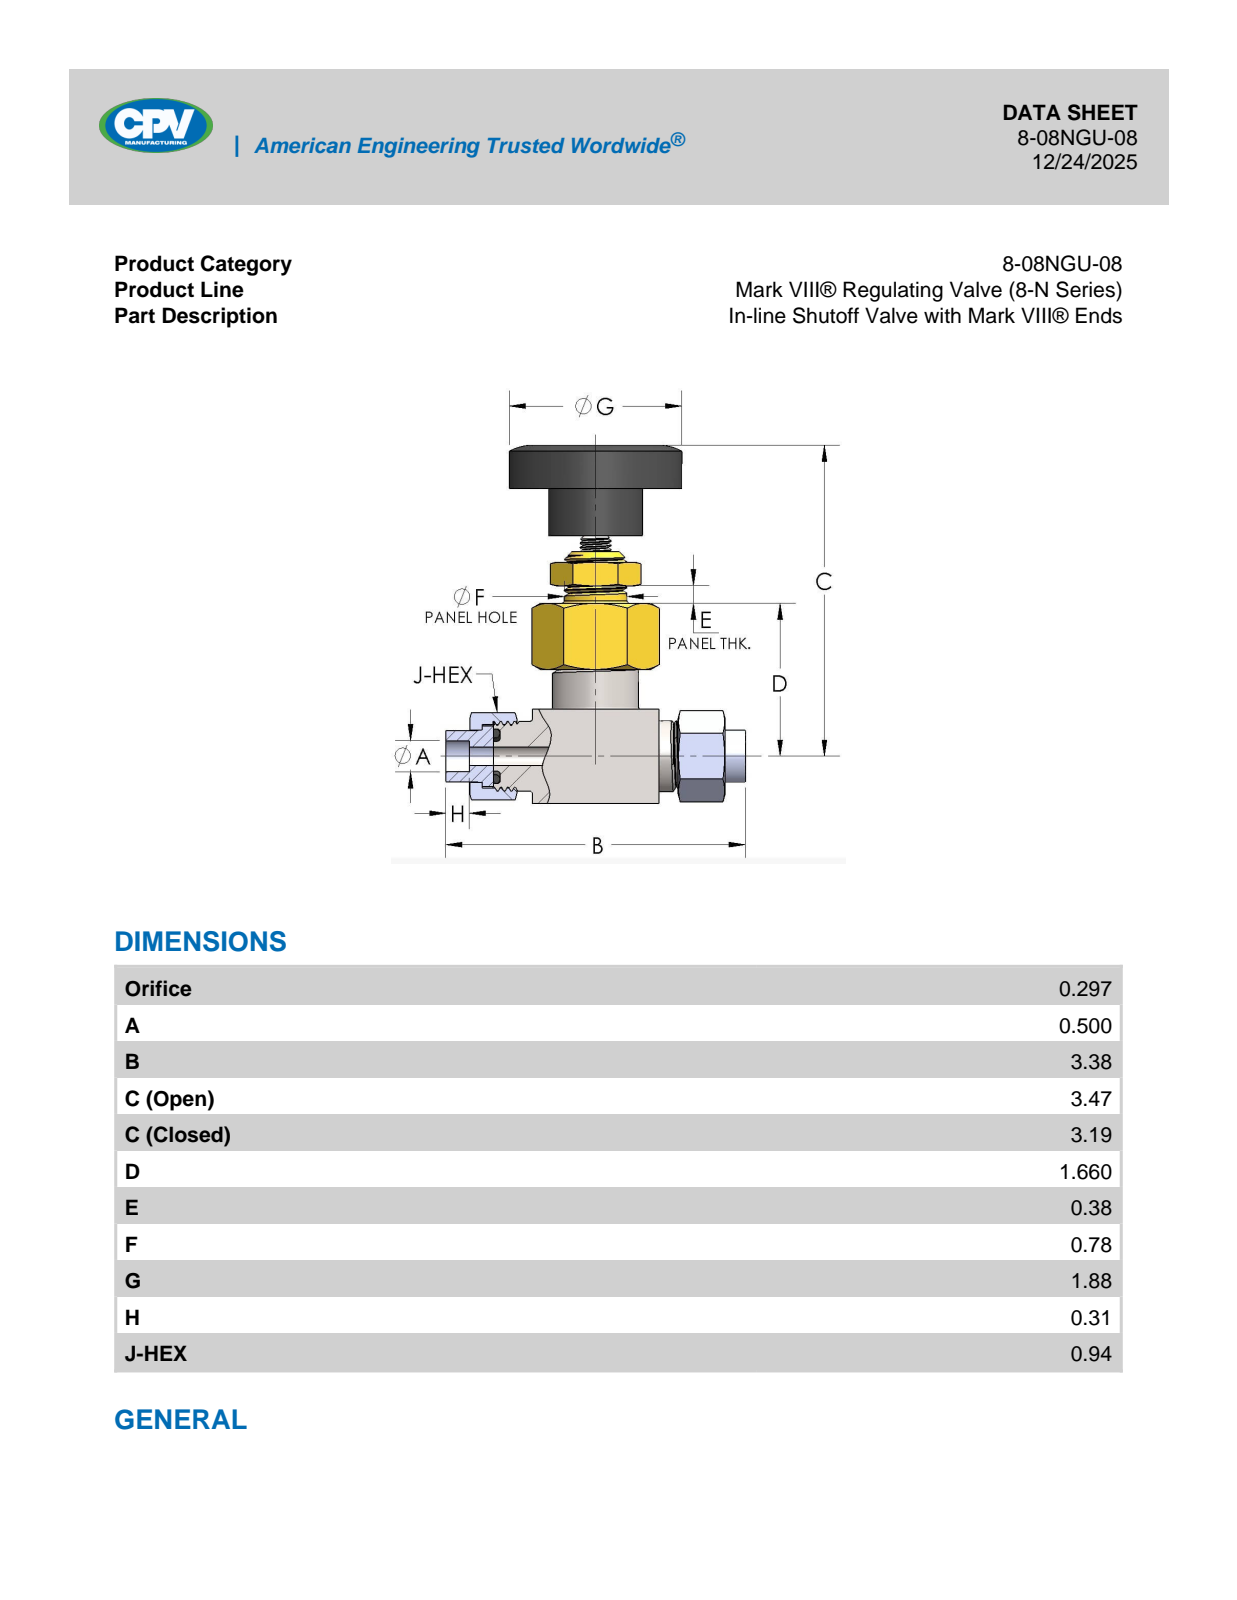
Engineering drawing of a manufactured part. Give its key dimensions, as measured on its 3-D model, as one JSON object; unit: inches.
{"part_name": "8-08SGU-08", "step_written_by": "SolidWorks 2018 (AUTOMOTIVE_DESIGN)", "units": "inches", "bodies": {"solids": 1, "faces": 169, "planar": 56, "cylindrical": 43, "other": 70}, "overall_size": [3.768, 3.38, 1.88], "volume_in3": 5.479, "surface_area_in2": 33.83, "round_holes": [[0.252, 1], [0.437, 1], [0.506, 1]], "round_bosses_or_shafts": [[1.88, 1], [1, 1], [0.996, 1], [0.808, 1], [0.748, 1], [0.65, 1], [0.312, 1], [0.25, 1]], "face_to_face_distances": [1.125, 0.31, 3.457, 3.767, 0.5, 1.128, 0.94, 0.093, 1.032, 0.095]}
